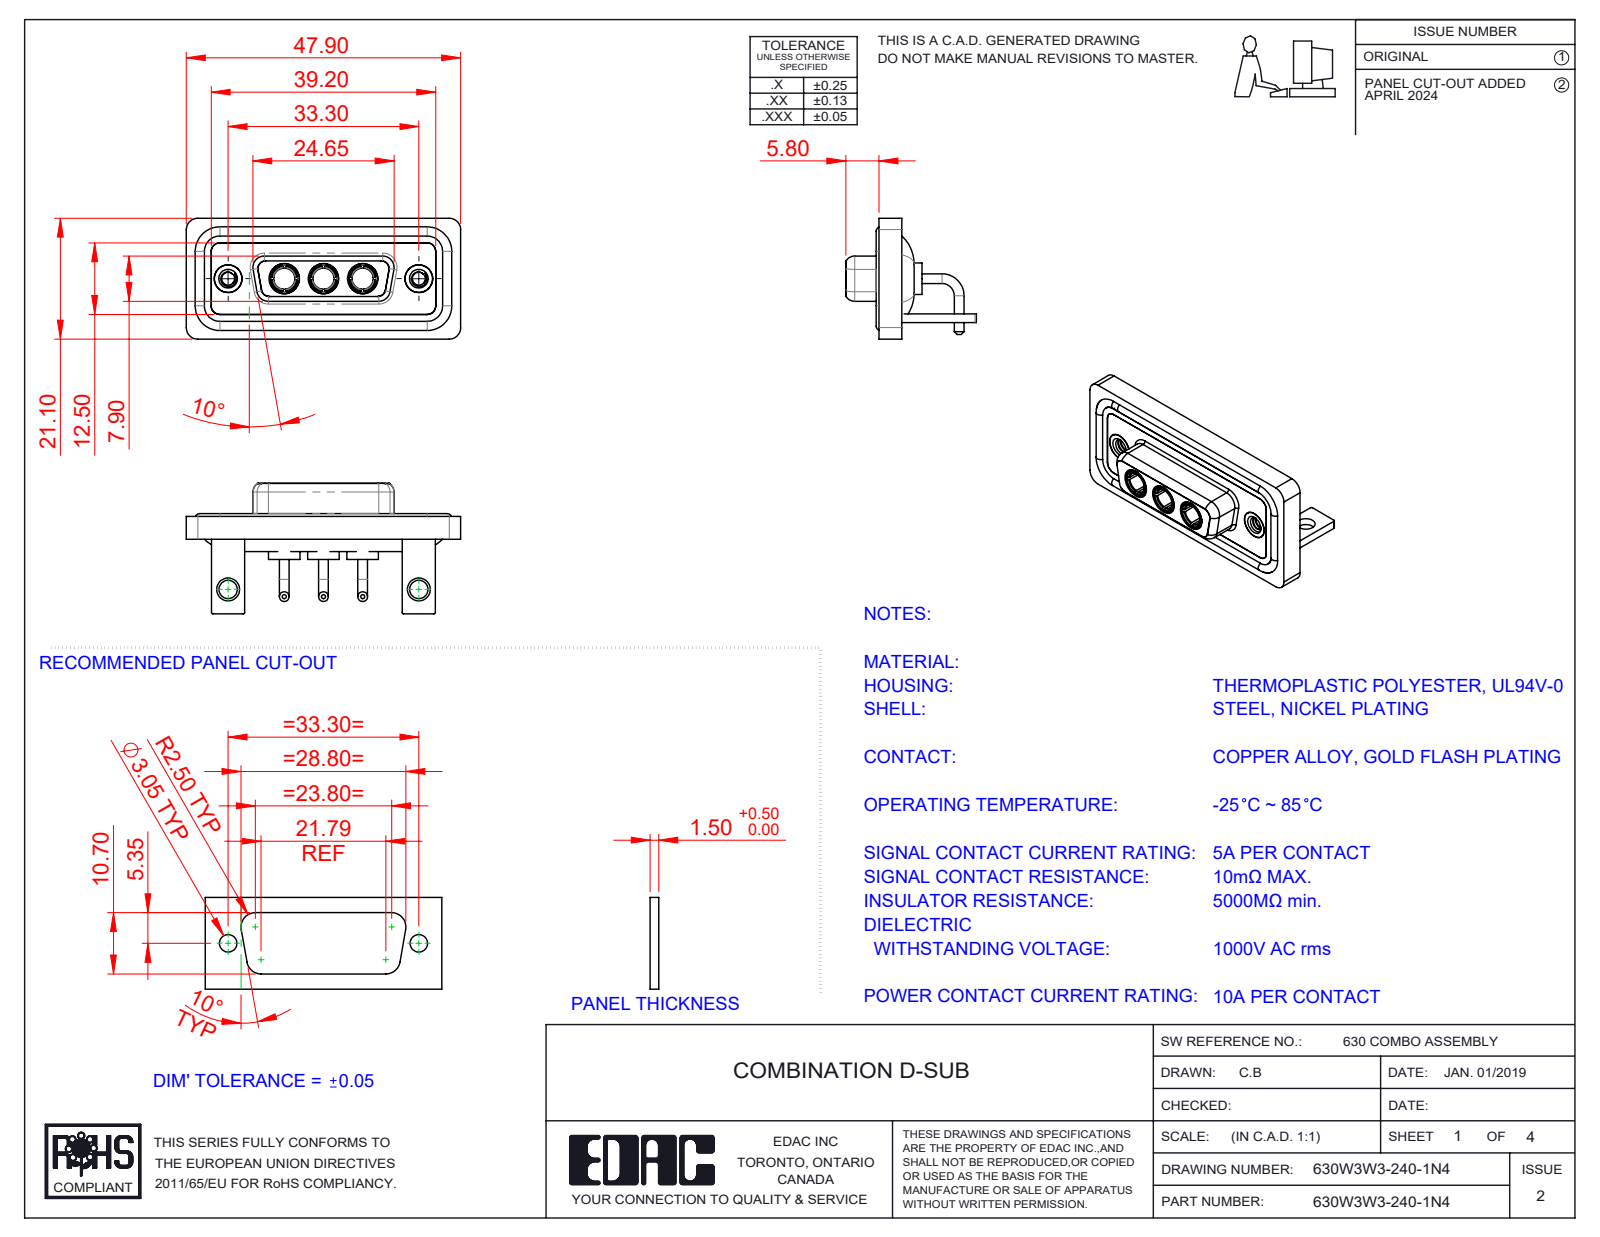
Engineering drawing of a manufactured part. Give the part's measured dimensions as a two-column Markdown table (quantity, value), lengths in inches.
| quantity | value |
| --- | --- |
| part name | 630Combo Shell Rear_15 Contacts; Power Socket_10A RA; 630Combo Threaded Rivet_2; 630Combo Housing_3W3 (+4 more) |
| STEP written by | SolidWorks 2023 (CONFIG_CONTROL_DESIGN) |
| units | inches |
| bodies | 15 solids, 668 faces (212 planar, 287 cylindrical, 169 other) |
| overall size | 1.886 × 0.898 × 0.831 |
| volume | 0.389 in³ |
| surface area | 16.36 in² |
| round holes (diameter × count) | 0.191 × 5, 0.146 × 3, 0.209 × 3, 0.089 × 2, 0.126 × 2, 0.157 × 2, 0.159 × 2, 0.197 × 2 |
| round bosses / shafts (diameter × count) | 0.067 × 6, 0.063 × 4, 0.217 × 3, 0.205 × 3, 0.195 × 3, 0.187 × 3, 0.148 × 3, 0.195 × 2 |
| partial cylindrical surfaces (radius × count) | 0.079 × 21, 0.059 × 18, 0.01 × 16, 0.053 × 12, 0.063 × 8, 0.02 × 5, 0.024 × 4, 0.026 × 4 |
| main face-to-face distances | 0.016, 0.114, 0.059, 0.071, 0.146, 0.043, 0.161, 0.063, 0.098, 0.055 |
| hole center spacings | 0.27, 0.386, 0.656, 0.925, 1.311, 0.539 |
